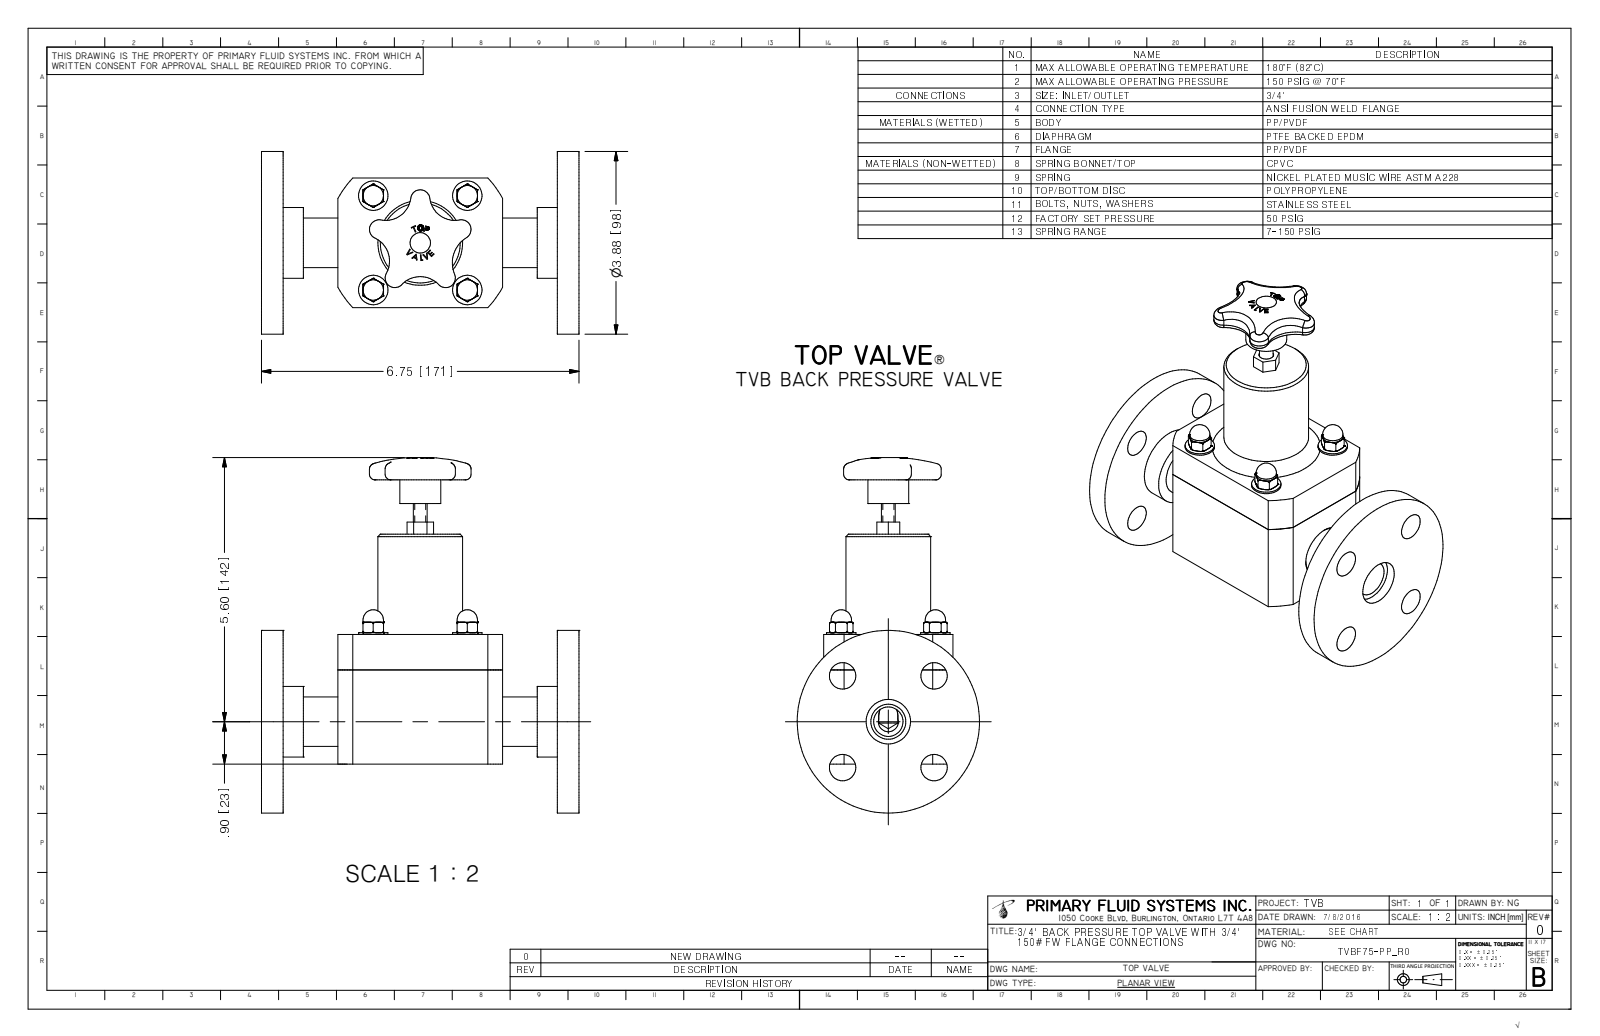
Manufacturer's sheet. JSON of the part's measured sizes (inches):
{"part_name": "TVBF75-PP_R0", "step_written_by": "Autodesk Inventor 2009 (AUTOMOTIVE_DESIGN)", "units": "inches", "bodies": {"solids": 1, "faces": 372, "planar": 155, "cylindrical": 64, "other": 153}, "overall_size": [7.539, 6.75, 3.875], "volume_in3": 43.67, "surface_area_in2": 158.3, "round_holes": [[0.175, 4], [0.56, 4], [0.281, 1], [0.742, 1], [0.945, 1]], "round_bosses_or_shafts": [[0.625, 4], [0.433, 4], [0.375, 4], [3.875, 1], [1.8, 1], [1.5, 1], [1.05, 1], [0.87, 1]], "partial_cylinders_radius": [[0.085, 5], [0.205, 5], [0.536, 4], [0.656, 4], [0.625, 1], [0.745, 1], [1.988, 1]], "face_to_face_distances": [0.46, 6.29, 6.75, 5.83, 1.625, 5.125, 1.165, 4.665, 2.75, 3.5], "hole_center_spacings": [1.375, 1.945, 2, 2.75, 2.828]}
